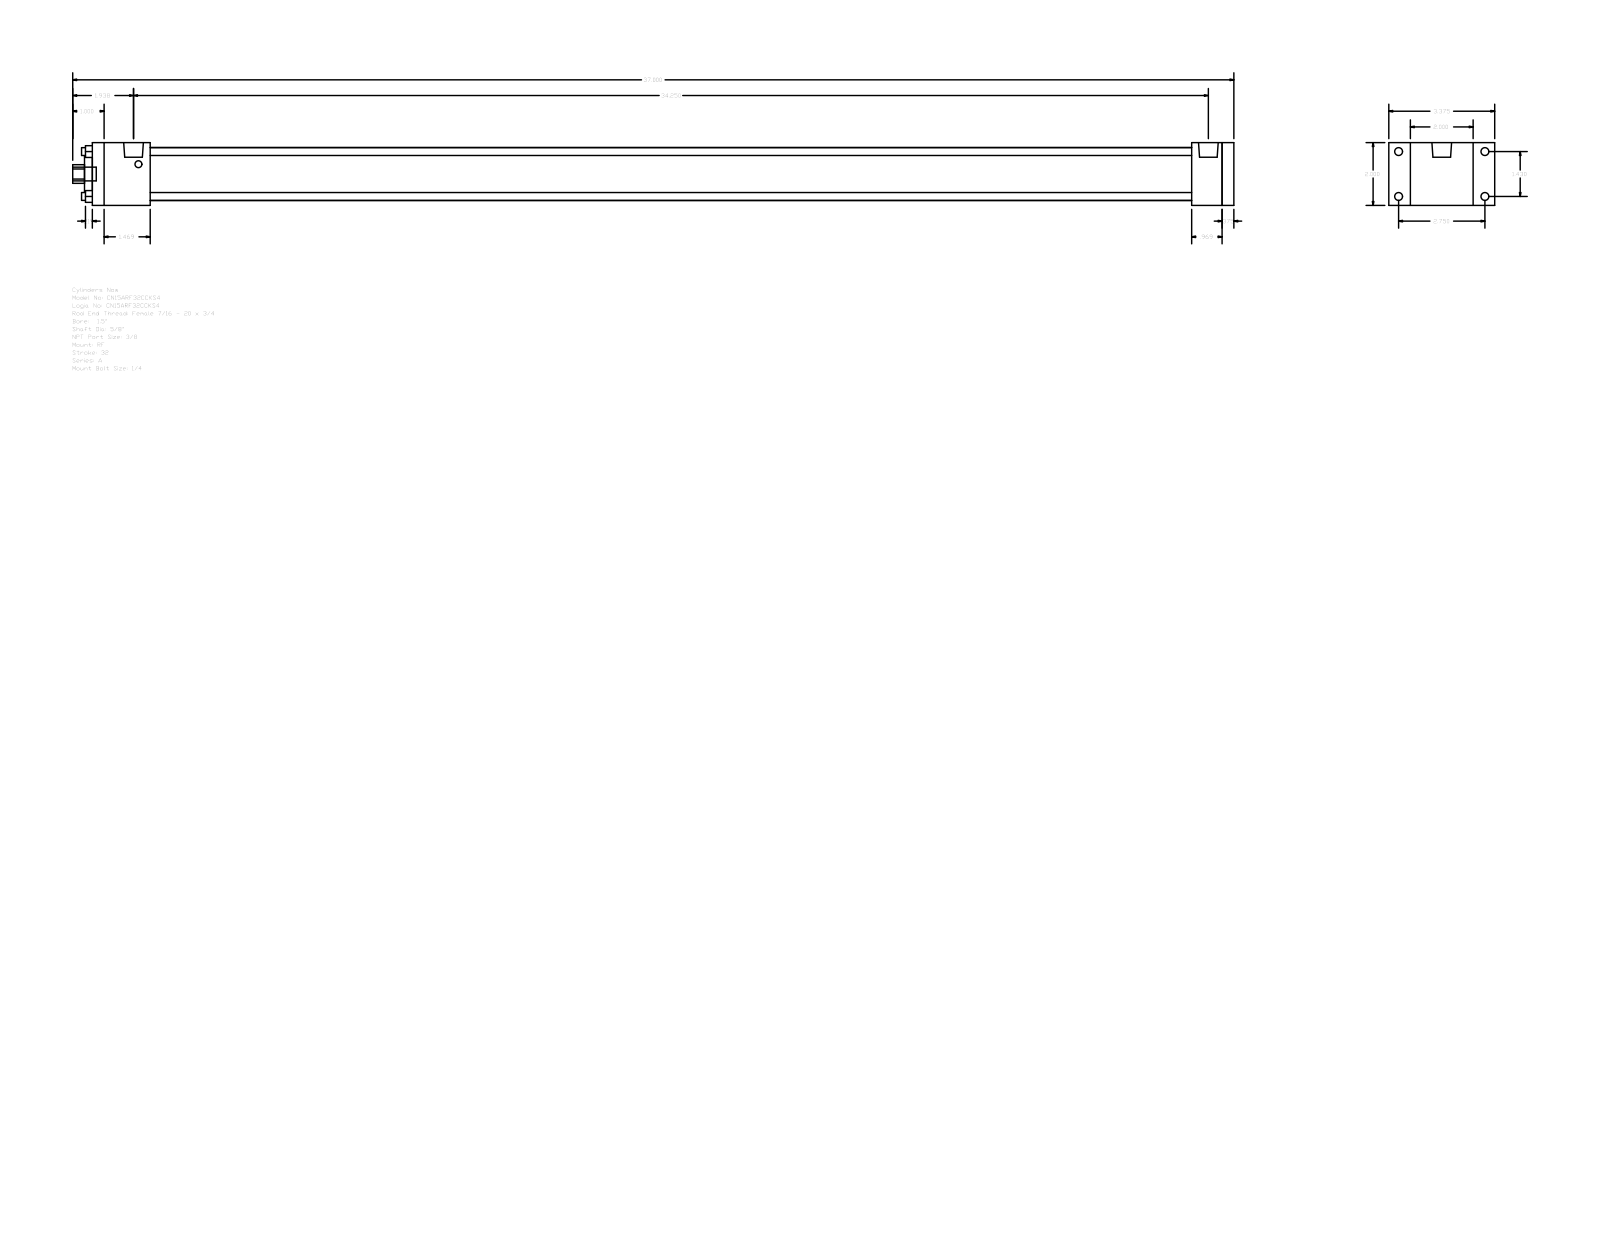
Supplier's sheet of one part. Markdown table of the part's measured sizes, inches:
| quantity | value |
| --- | --- |
| part name | A_RF__0150_0.625 |
| STEP written by | GSSL Pune (CONFIG_CONTROL_DESIGN) |
| units | inches |
| bodies | 0 solids, 92 faces (64 planar, 28 cylindrical, 0 other) |
| overall size | 37 × 3.375 × 2 |
| round holes (diameter × count) | 0.25 × 4, 0.625 × 1, 1.125 × 1, 1.69 × 1 |
| round bosses / shafts (diameter × count) | 0.25 × 4, 0.219 × 4, 0.627 × 2, 0.437 × 1 |
| partial cylindrical surfaces (radius × count) | 0.297 × 1 |
| main face-to-face distances | 2, 0.375, 36.375, 36, 35.031, 0.969, 1.344, 1.844, 33.187, 34.156 |
| hole center spacings | 1.011, 1.43, 2.022 |
